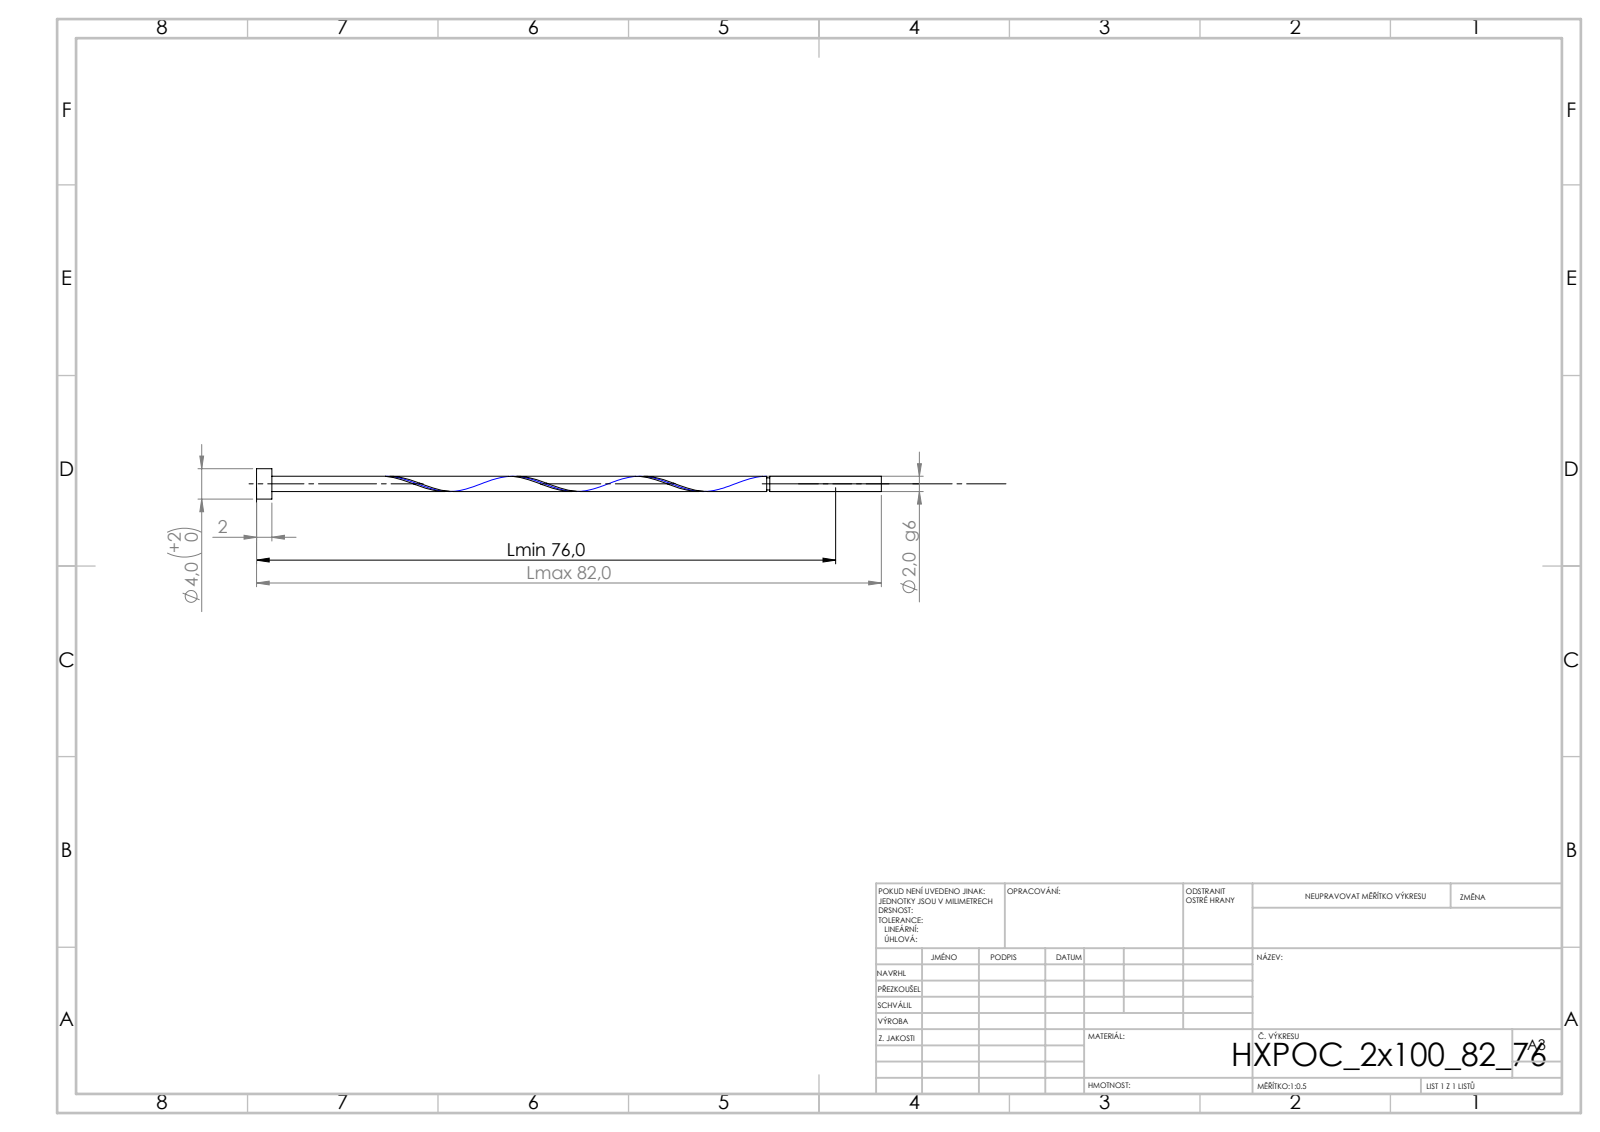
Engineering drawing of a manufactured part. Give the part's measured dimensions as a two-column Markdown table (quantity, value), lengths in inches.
| quantity | value |
| --- | --- |
| STEP written by | SolidWorks 2019 (CONFIG_CONTROL_DESIGN) |
| units | inches |
| bodies | 1 solid, 21 faces (6 planar, 14 cylindrical, 1 other) |
| overall size | 3.228 × 0.157 × 0.157 |
| volume | 0.017 in³ |
| surface area | 0.876 in² |
| round bosses / shafts (diameter × count) | 0.157 × 1, 0.079 × 1, 0.063 × 1 |
| main face-to-face distances | 0.079, 3.228, 3.15, 2.652, 2.573, 0.577, 2.636, 2.557, 0.016, 0.593 |
